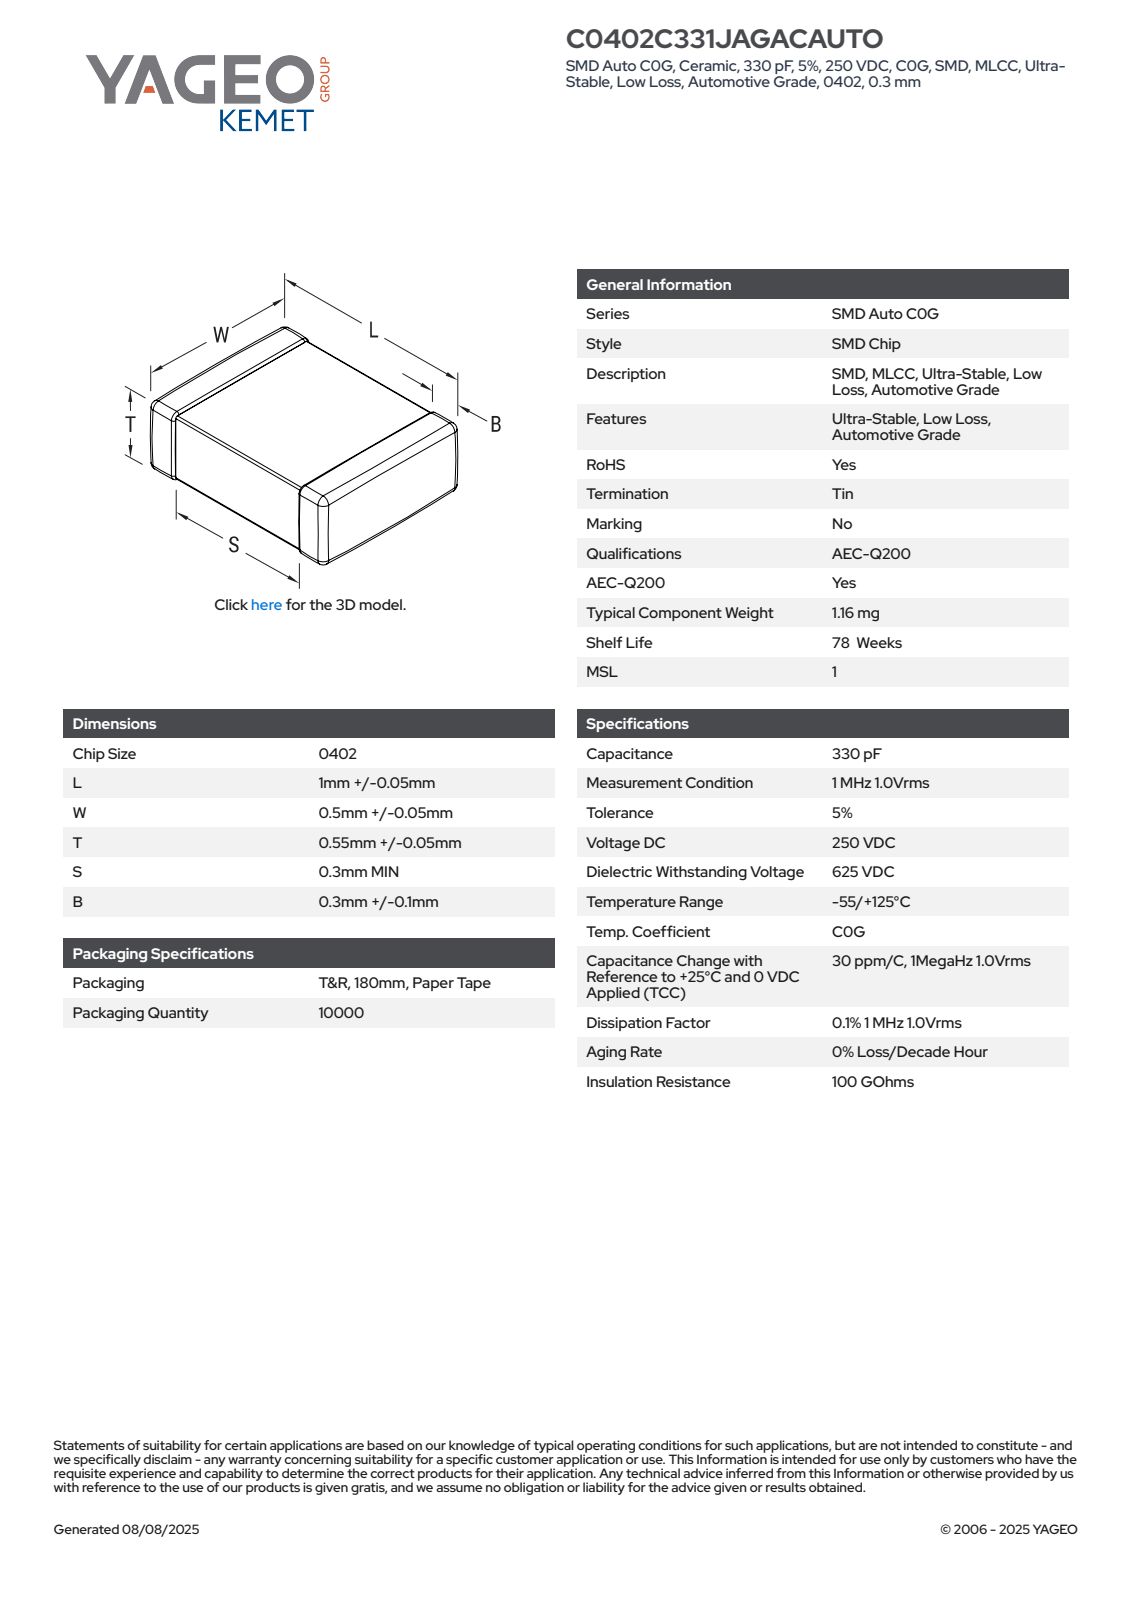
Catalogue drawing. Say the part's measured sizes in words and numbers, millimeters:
The part is named "CCS_CCSTD_0402_L1.05W0.55T0.6B0.3". Its 3-D file was written by "SolidWorks 2021 (AUTOMOTIVE_DESIGN)". It is 4 solids with 125 faces: 71 planar, 38 cylindrical and 16 other. Overall it measures 1.05 by 0.6 by 0.55 millimeters. Its volume is 0.34 cubic millimeters and its surface area 3 square millimeters. The main face-to-face distances are 0.55, 0.6, 1.05, 0.59, 0.54, 0.53, 0.58, 0.49, 0.56, 0.57.
